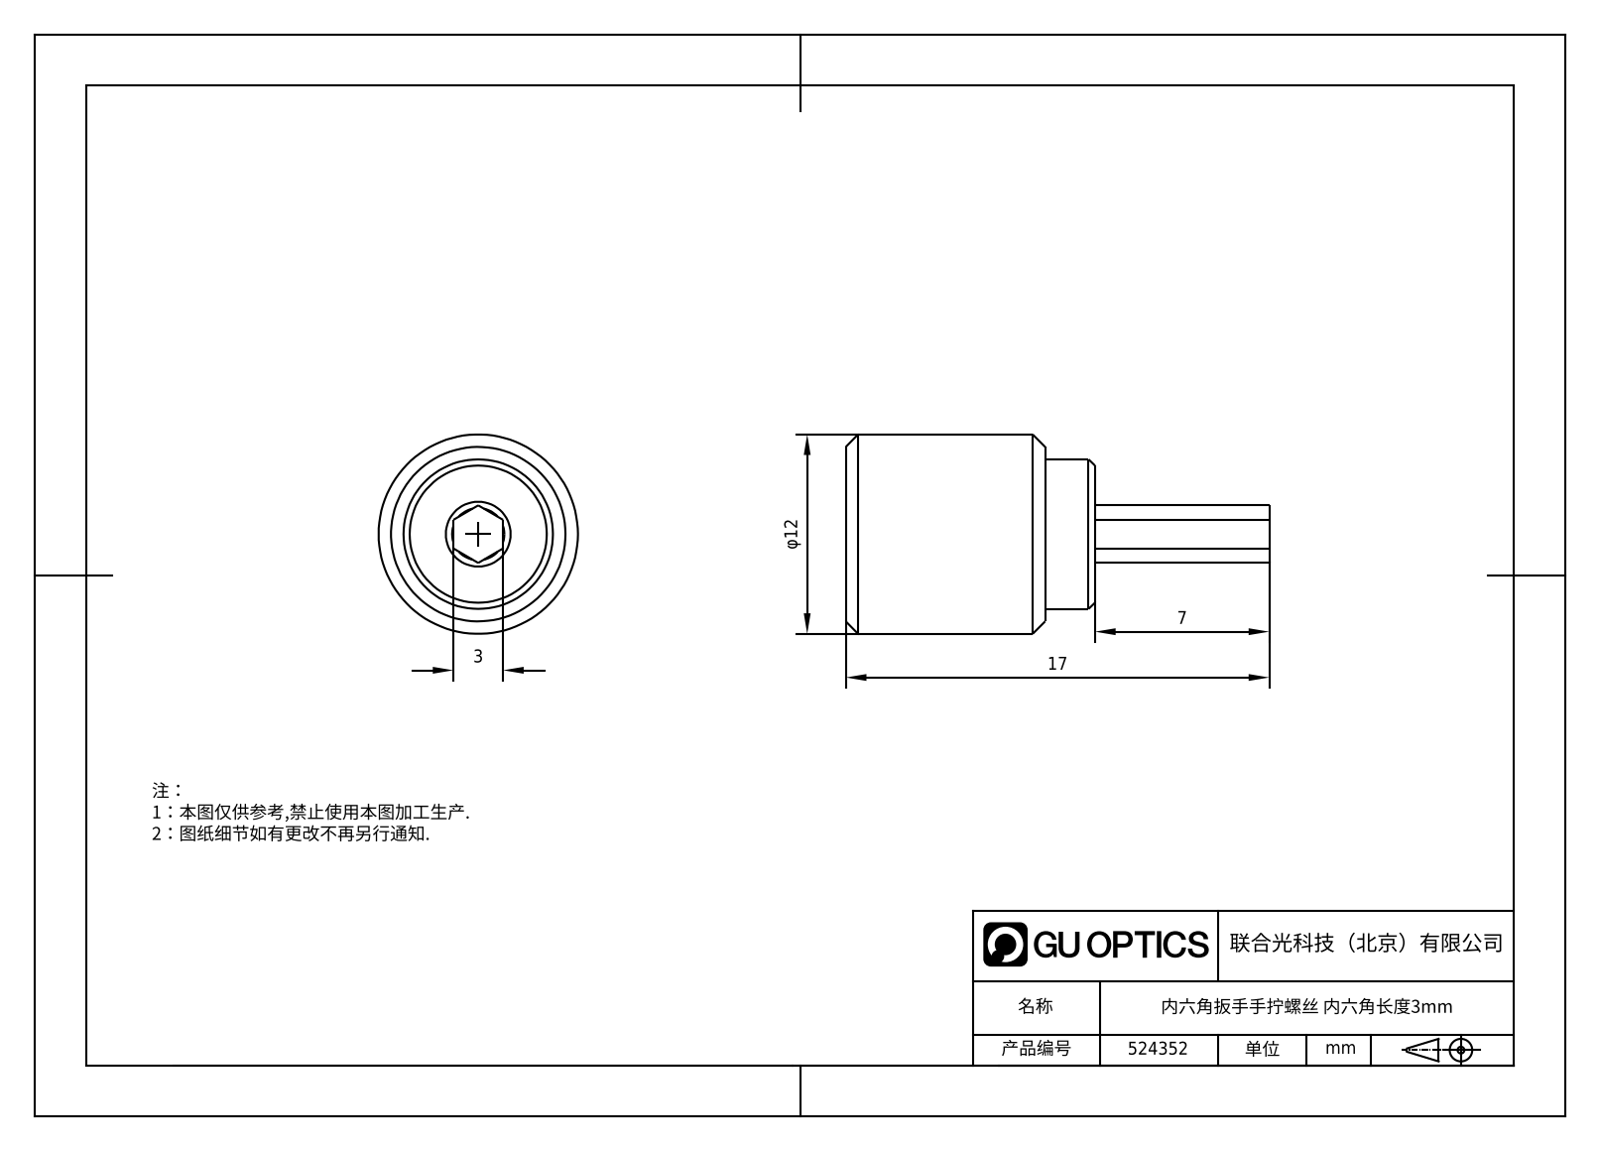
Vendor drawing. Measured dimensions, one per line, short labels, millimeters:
name: 1.8.4.3.2_直杆式3x3mm六角扳手，长度11mm，零部件
written by: SolidWorks 2021 (CONFIG_CONTROL_DESIGN)
unit: mm
bodies: 2 solids, 26 faces (12 planar, 6 cylindrical, 8 other)
size: 17 × 12 × 12
volume: 1 107 mm³; area: 731 mm²
holes: 1× ⌀3.1
bosses: 1× ⌀12, 1× ⌀10
face distances: 10, 3, 2, 8, 6, 4, 17, 11, 9, 7
